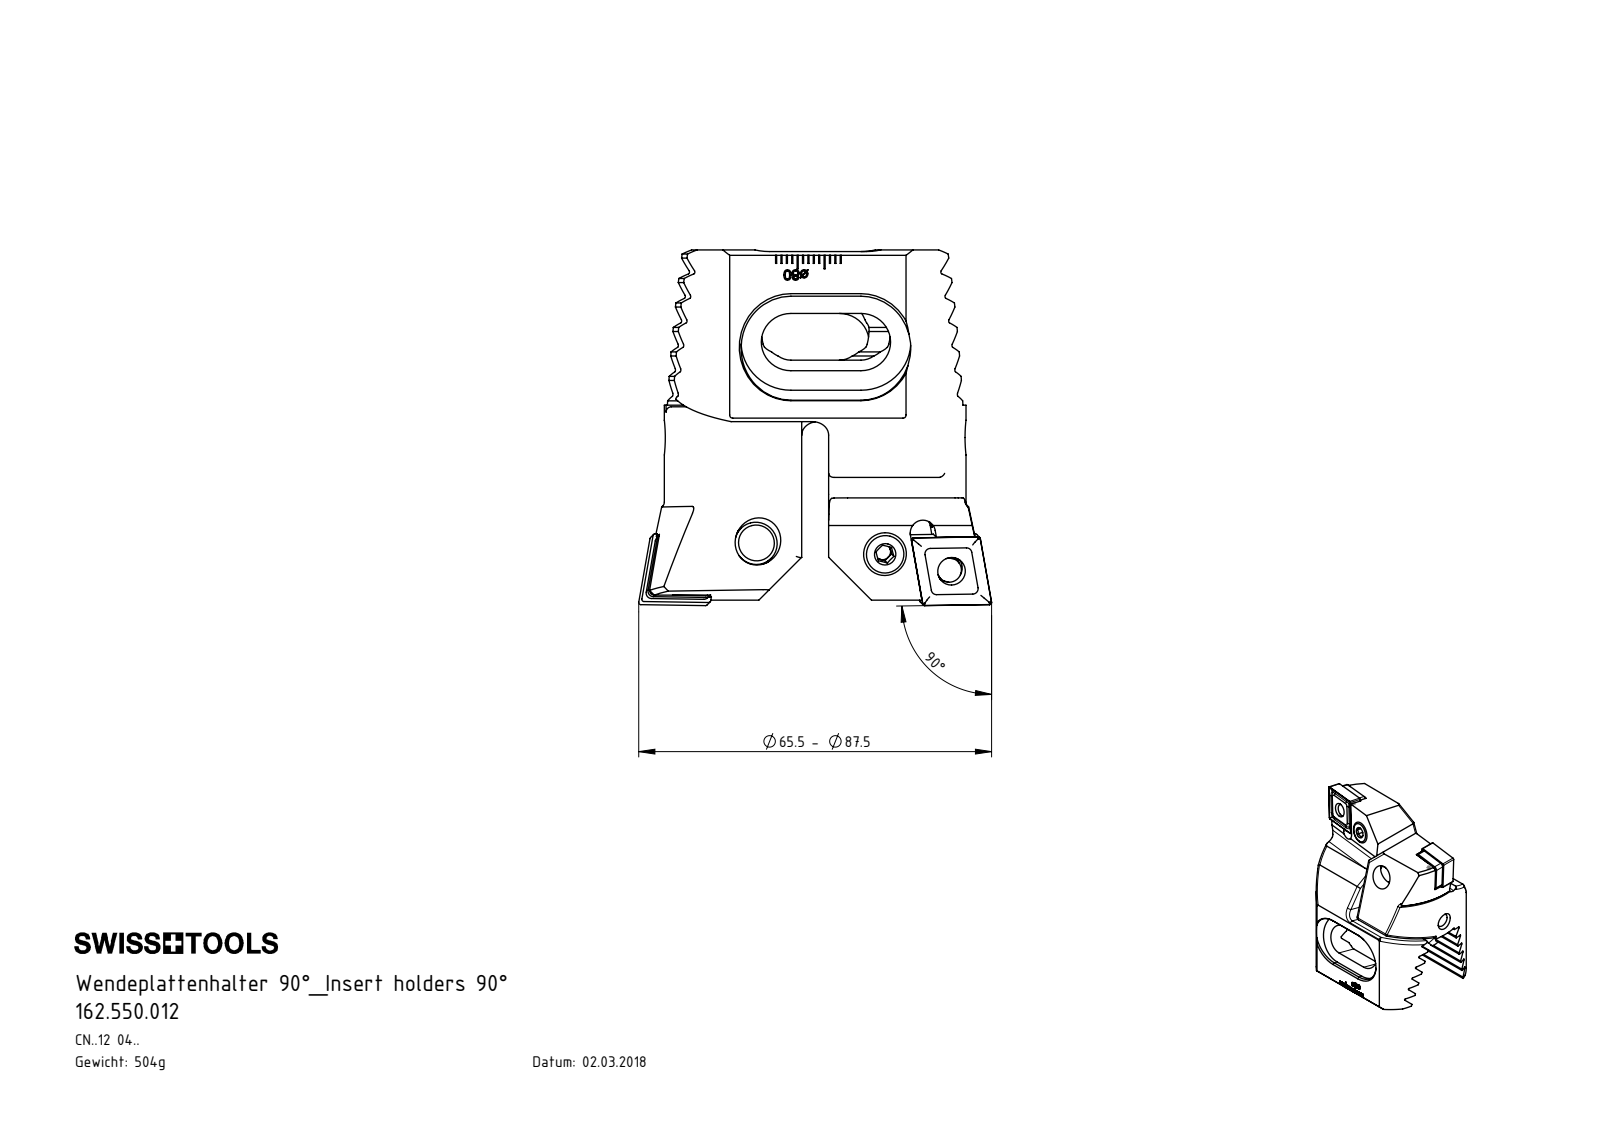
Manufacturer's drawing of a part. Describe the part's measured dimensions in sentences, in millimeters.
The part is named "CNMG120404; WCD-ER1.101.000; WCD-ER2.101.003_A; Z55-ER3.001.020 (+5 more)". Its 3-D file was written by "SolidWorks 2017 (CONFIG_CONTROL_DESIGN)". It is 14 solids with 876 faces: 424 planar, 170 cylindrical and 282 other. Overall it measures 65.98 by 65.5 by 44.2 millimeters. Its volume is 63 396 cubic millimeters and its surface area 26 305 square millimeters. Round holes: 2 of diameter 2, 2 of diameter 5.16, 2 of diameter 6.4, 2 of diameter 7, 2 of diameter 8.4, 1 of diameter 5. Round bosses or shafts: 2 of diameter 8, 2 of diameter 7.9, 2 of diameter 6.4, 2 of diameter 4.5, 2 of diameter 3.55, 1 of diameter 6, 1 of diameter 4. Partial cylindrical surfaces (rounded edges, fillets, slot ends): 22 of radius 1, 12 of radius 0.34, 8 of radius 0.4, 6 of radius 2.5, 6 of radius 3, 4 of radius 5.5, 4 of radius 9.25, 4 of radius 12. The main face-to-face distances are 4.07, 8.14, 12.21, 16.28, 20.35, 7.85, 1.69, 5, 0.5, 44.2. The hole center spacings are 12.81, 12.86, 16, 30.9.
